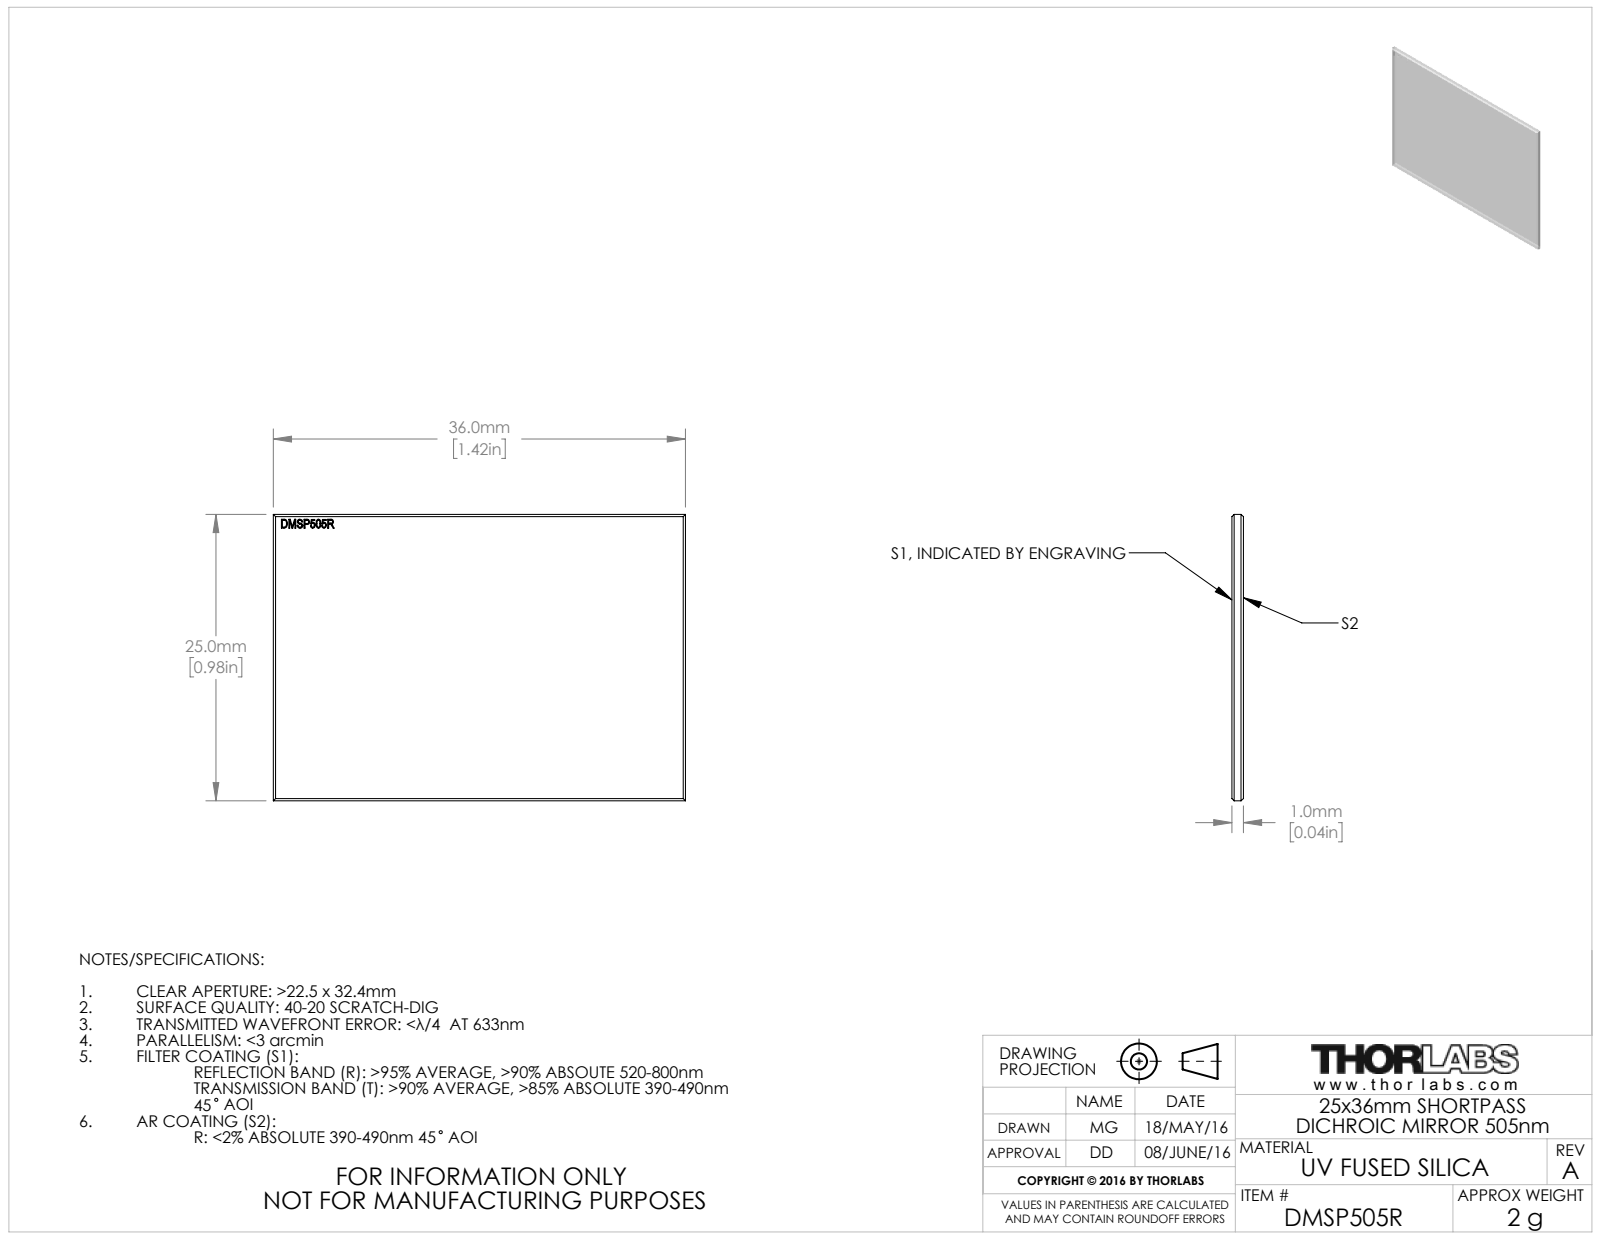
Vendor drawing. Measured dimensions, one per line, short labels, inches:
name: TTN045178-E0W
written by: SolidWorks 2016 (CONFIG_CONTROL_DESIGN)
unit: in
bodies: 1 solid, 140 faces (81 planar, 0 cylindrical, 59 other)
size: 1.417 × 0.984 × 0.039
volume: 0.055 in³; area: 2.936 in²
face distances: 0.039, 0.984, 0.713, 1.417, 1.019, 0.039, 0.028, 0.078, 0.031, 0.021
